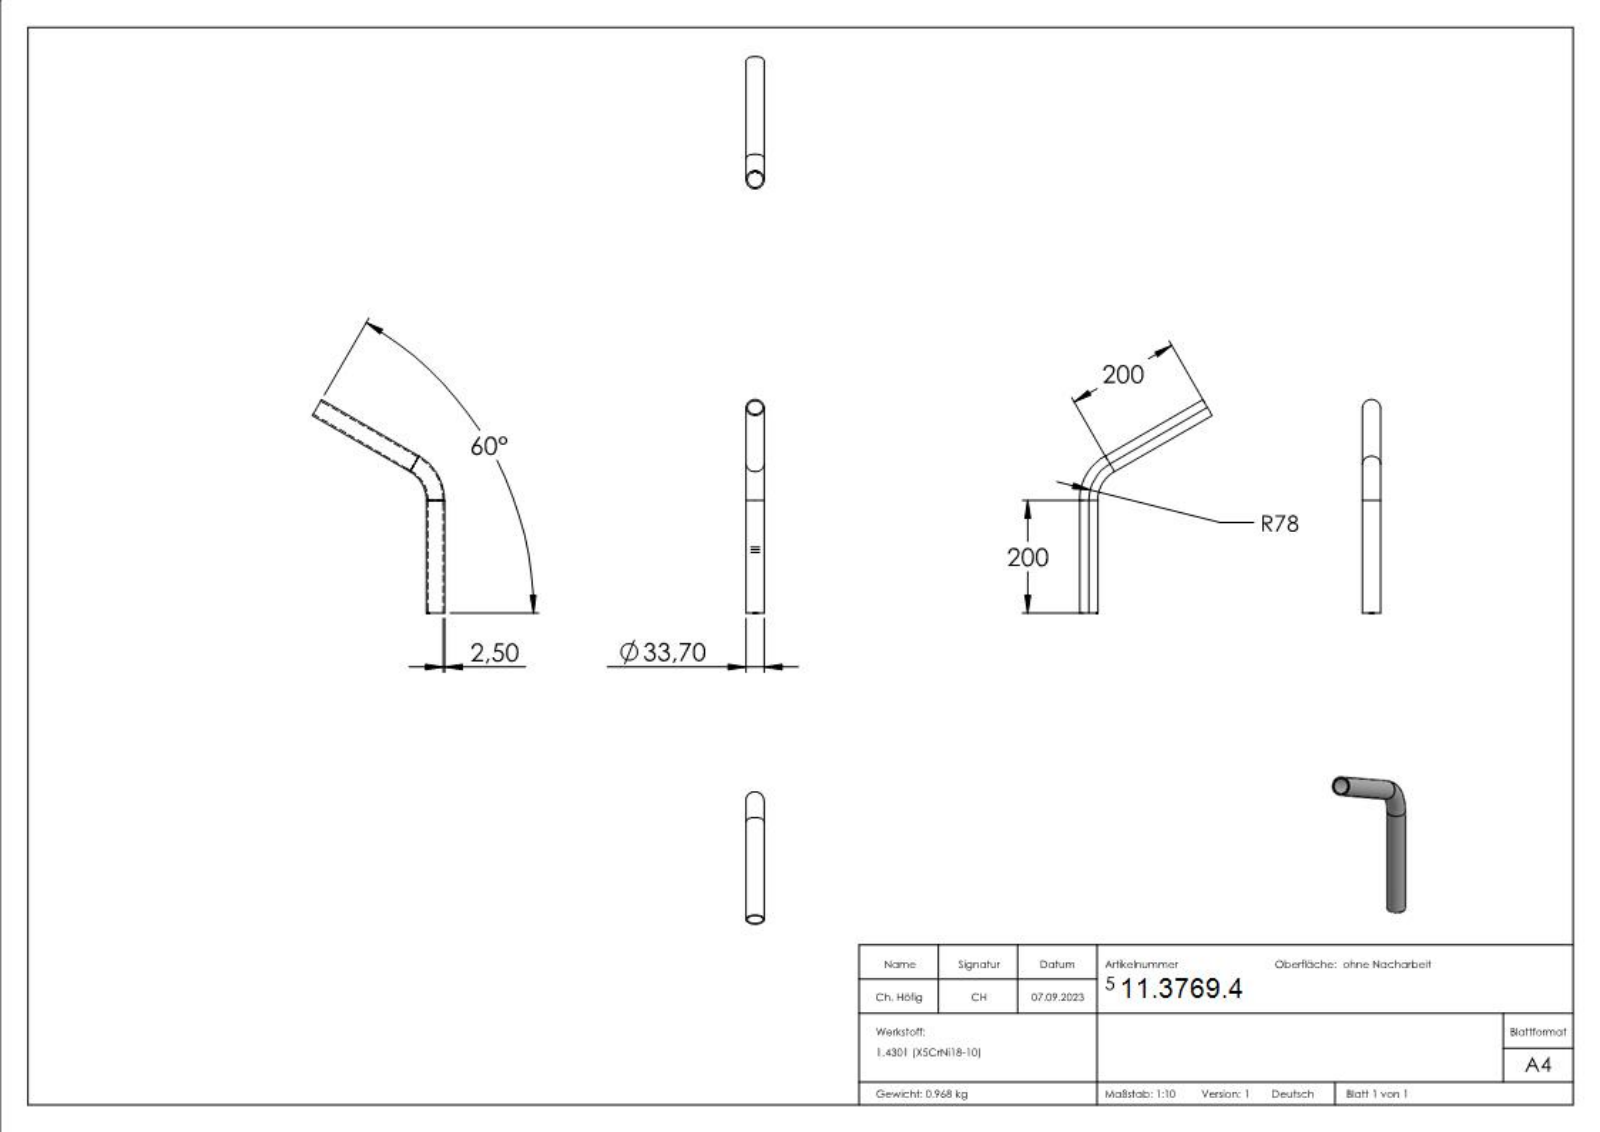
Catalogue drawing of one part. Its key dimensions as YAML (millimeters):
part_name: "55121-060"
step_written_by: "SolidWorks 2015 (CONFIG_CONTROL_DESIGN)"
units: millimeters
bodies: {solids: 1, faces: 225, planar: 93, cylindrical: 31, other: 101}
overall_size: [382.14, 237.48, 33.7]
volume: 118033
surface_area: 94927
round_holes:
  - {diameter: 28.7, count: 2}
round_bosses_or_shafts:
  - {diameter: 33.7, count: 2}
partial_cylinders:
  - {radius: 14.45, count: 1}
face_to_face_distances: [2.02, 0.39, 1.12, 2.42, 2.04, 0.38, 2.97, 1.92, 4.44, 2.4]
